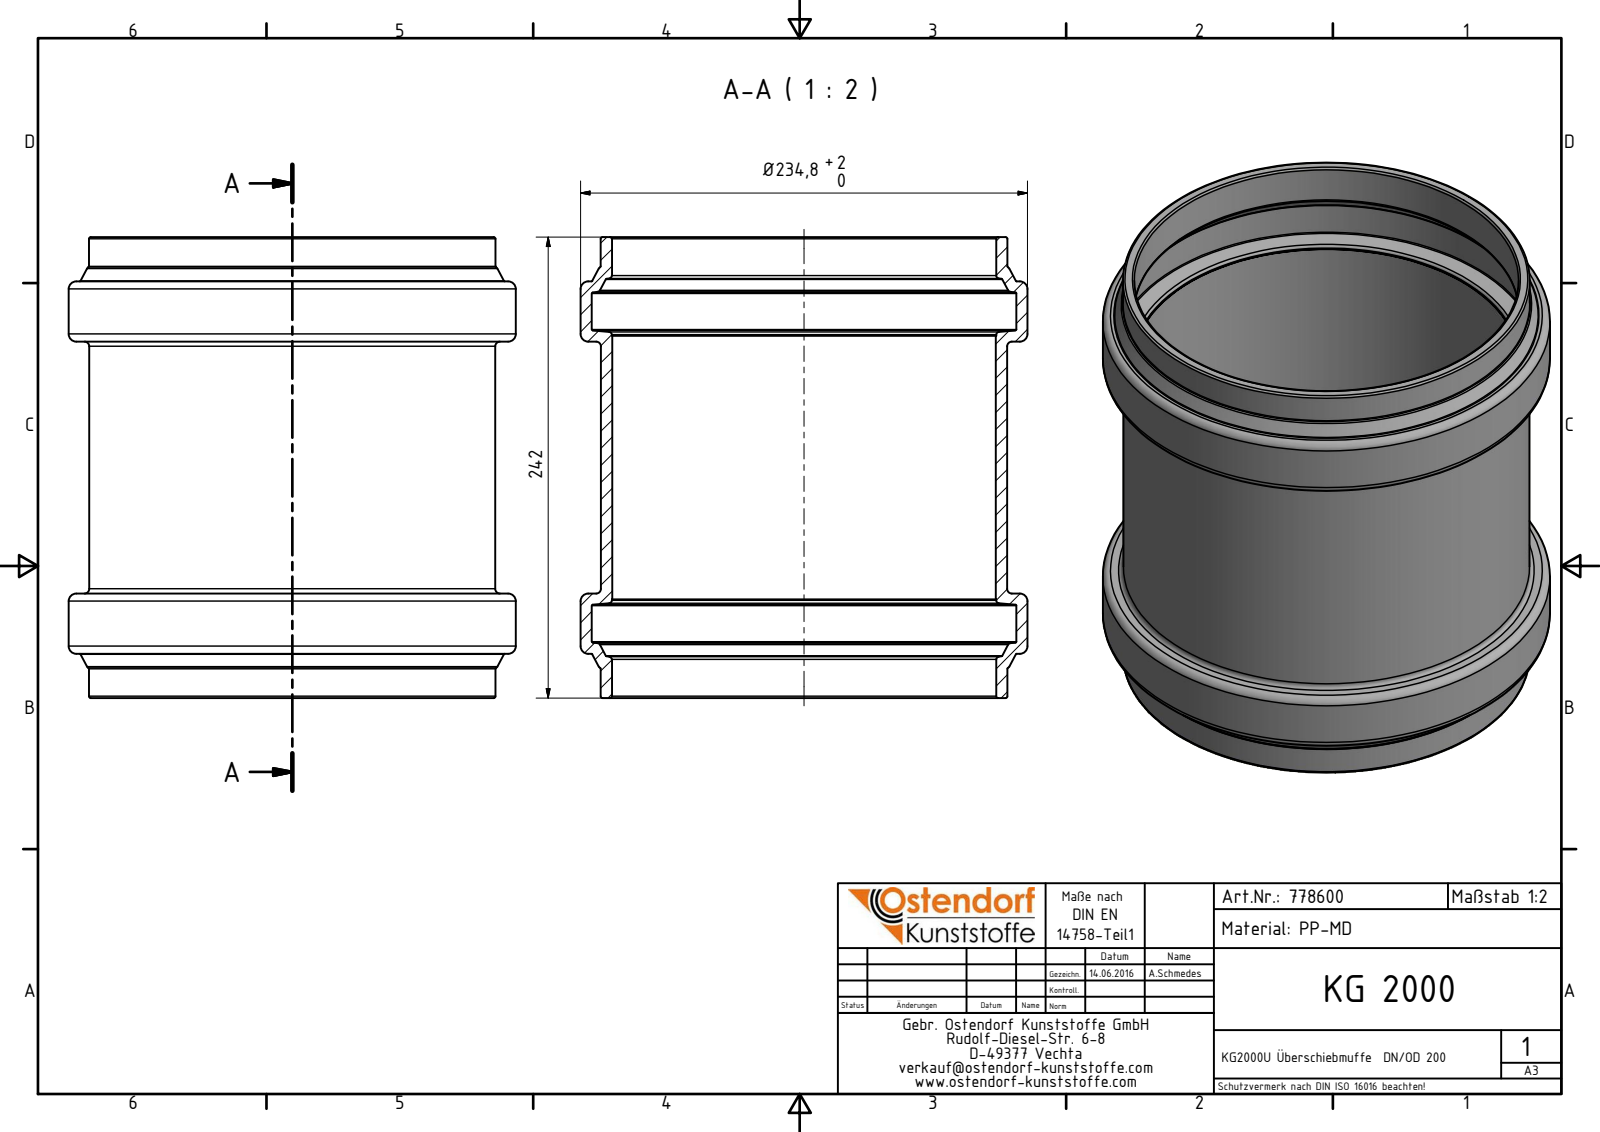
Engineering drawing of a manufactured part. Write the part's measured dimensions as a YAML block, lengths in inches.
part_name: "778600 KG2000U Überschiebmuffe DN_OD 200"
step_written_by: "Autodesk Inventor 2016 (AUTOMOTIVE_DESIGN)"
units: inches
bodies: {solids: 1, faces: 58, planar: 8, cylindrical: 12, other: 38}
overall_size: [9.528, 9.244, 9.244]
volume: 66.21
surface_area: 572.7
round_holes:
  - {diameter: 7.933, count: 1}
  - {diameter: 7.945, count: 1}
  - {diameter: 8.78, count: 1}
round_bosses_or_shafts:
  - {diameter: 9.244, count: 1}
  - {diameter: 8.409, count: 1}
  - {diameter: 8.398, count: 1}
face_to_face_distances: [2.161, 7.366, 5.205, 9.528, 0.917, 8.61, 1.244, 6.449, 7.693, 2.042]
